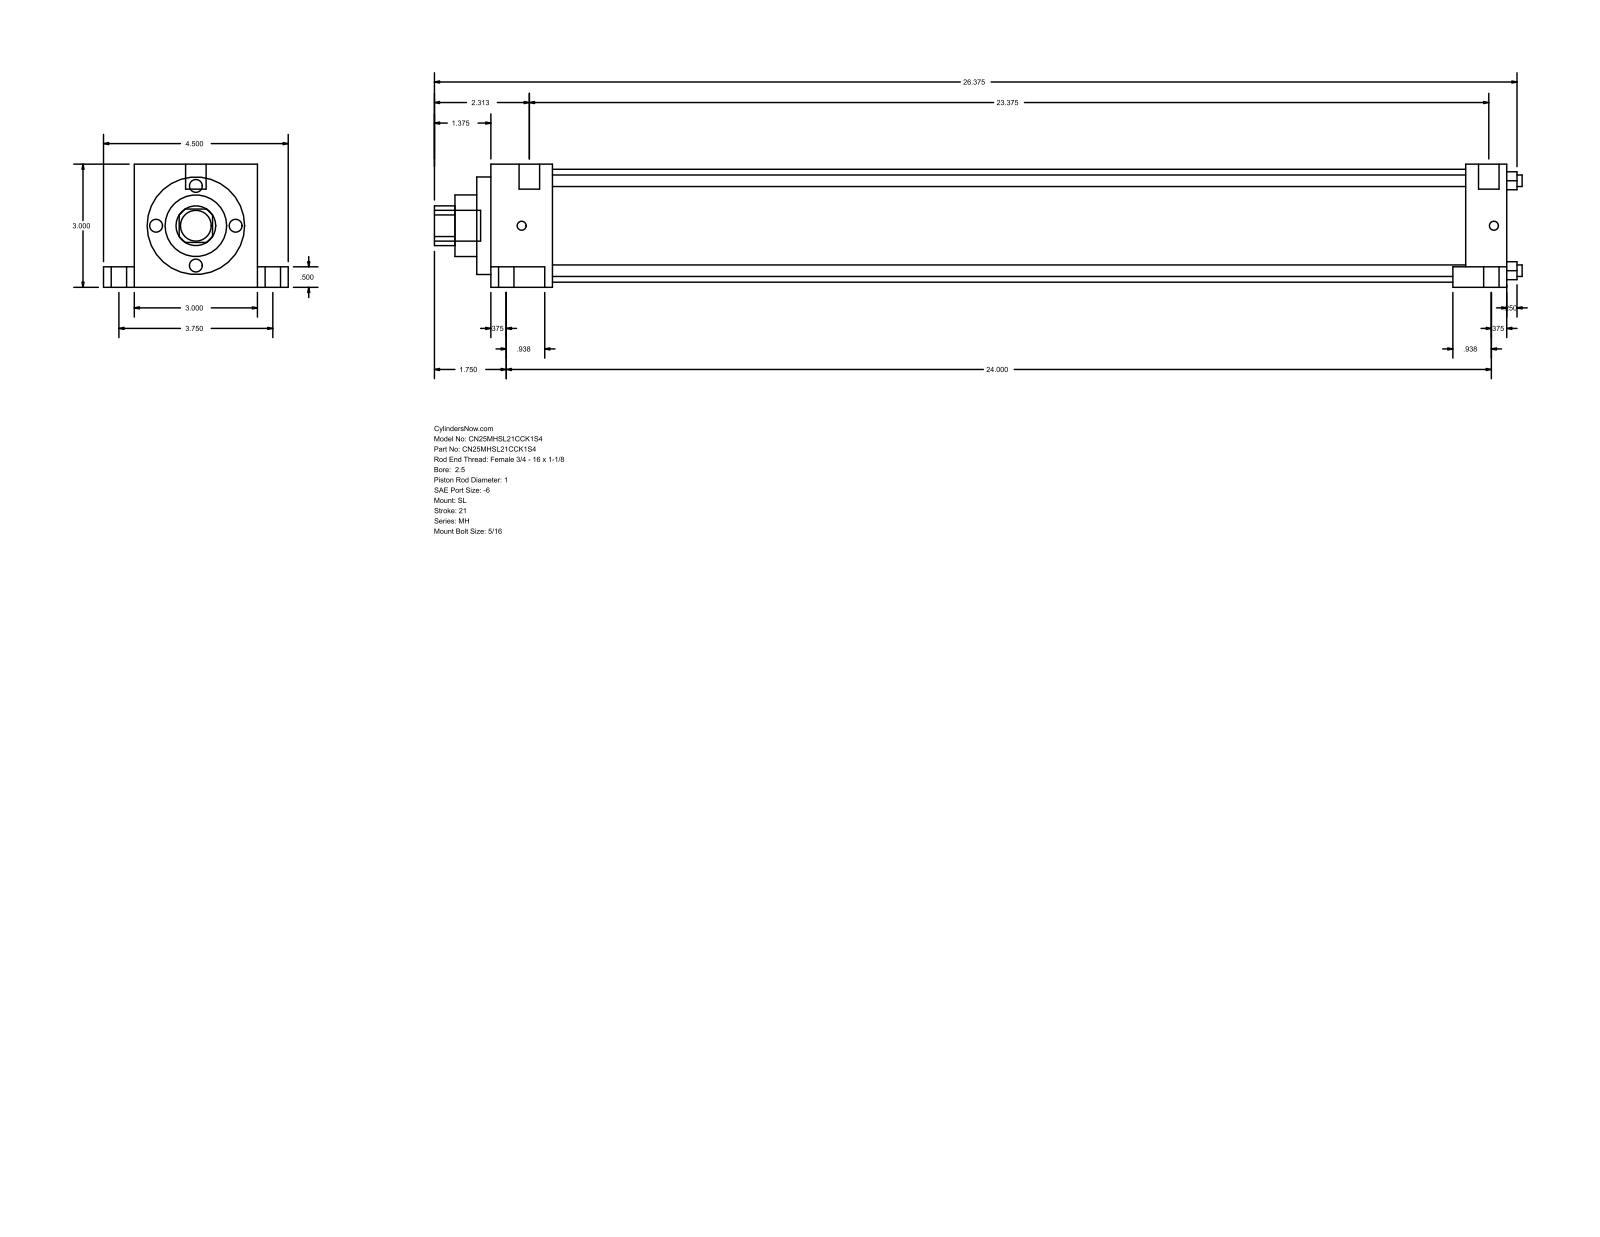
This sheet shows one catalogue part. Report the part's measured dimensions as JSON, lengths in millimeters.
{"part_name": "MH_SL__0250_1", "step_written_by": "GSSL Pune (CONFIG_CONTROL_DESIGN)", "units": "millimeters", "bodies": {"solids": 0, "faces": 86, "planar": 61, "cylindrical": 25, "other": 0}, "overall_size": [673.1, 114.3, 76.2], "round_holes": [[7.14, 4], [25.4, 1], [38.1, 1], [60.33, 1], [69.85, 1]], "round_bosses_or_shafts": [[15.88, 2], [9.53, 2], [5.56, 2], [19.05, 1], [12.7, 1]], "partial_cylinders_radius": [[12.29, 1]], "face_to_face_distances": [76.2, 25.41, 611.98, 637.39, 12.7, 63.5, 19.05, 95.25, 13.49, 625.47], "hole_center_spacings": [39.33, 55.62, 78.66]}
